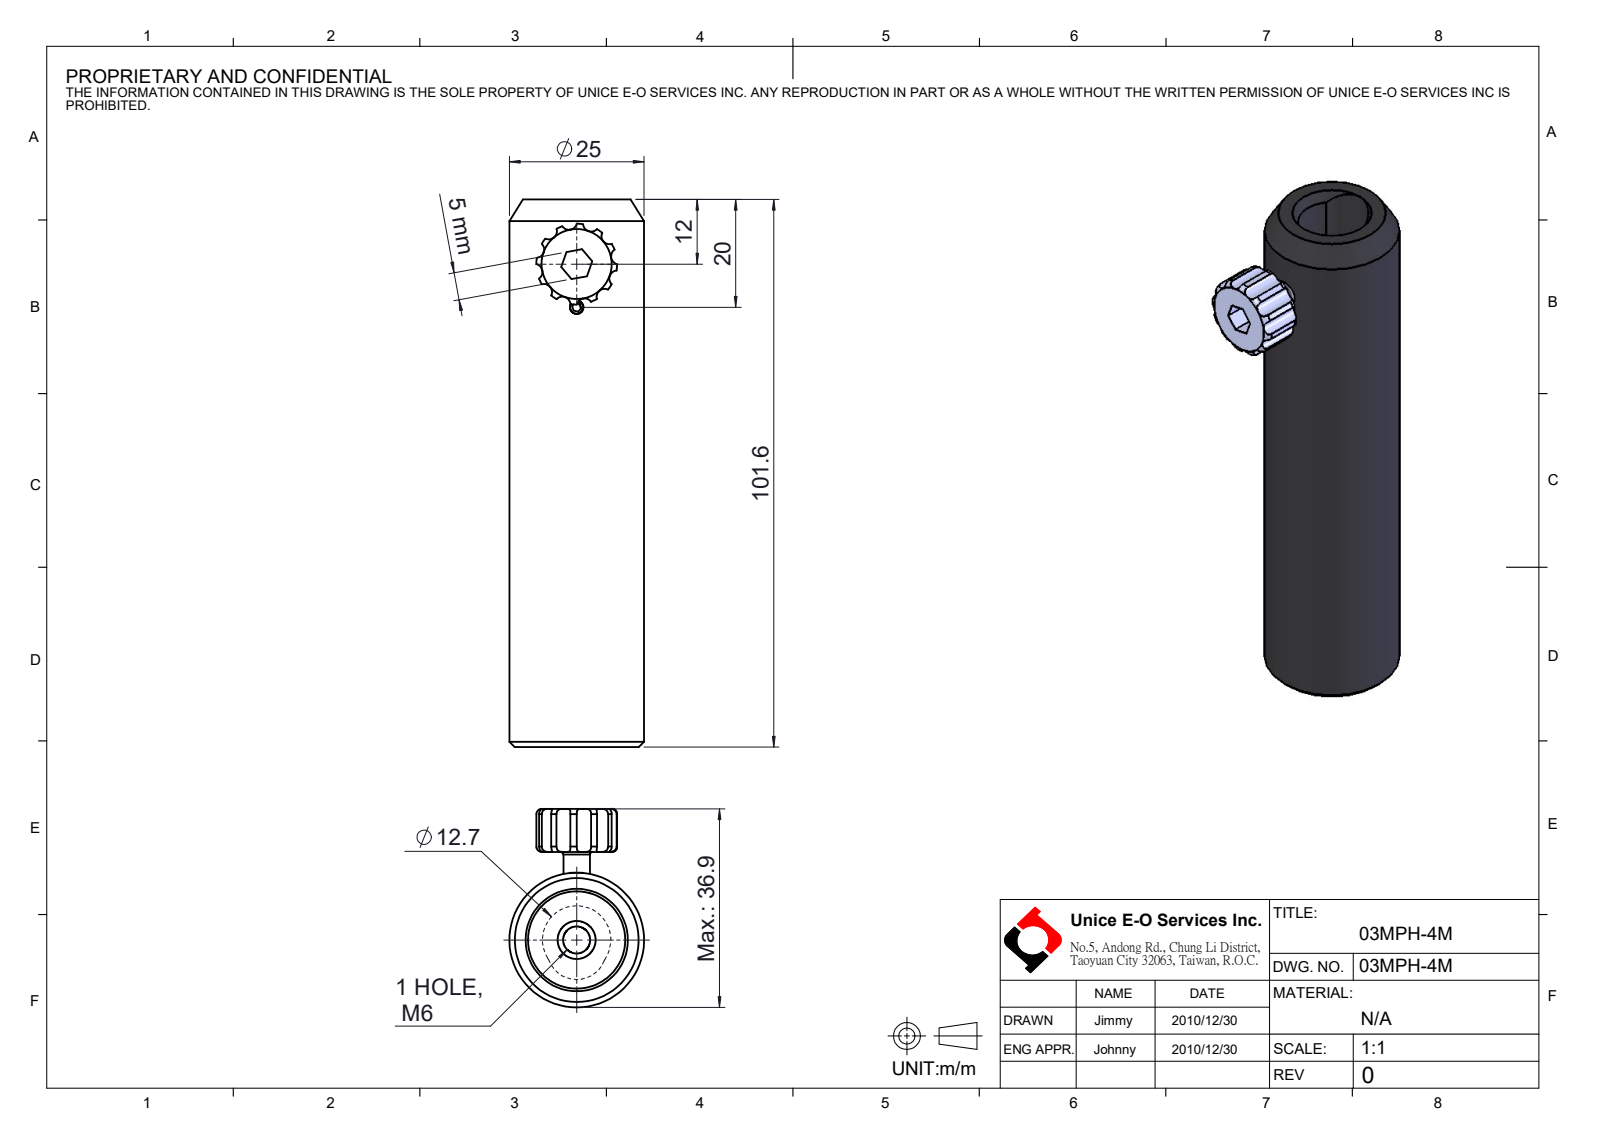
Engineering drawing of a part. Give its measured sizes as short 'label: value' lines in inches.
name: 03MPH-4M
written by: SolidWorks 2016 (CONFIG_CONTROL_DESIGN)
unit: in
bodies: 0 solids, 95 faces (17 planar, 40 cylindrical, 38 other)
size: 4 × 1.451 × 0.984
holes: 1× ⌀0.197, 1× ⌀0.748
bosses: 1× ⌀0.984, 1× ⌀0.194
rounds: 12× R0.059, 1× R0.217, 1× R0.25, 1× R0.295
face distances: 4, 0.315, 0.201, 0.165, 0.15, 0.152, 0.317, 0.467, 0.059
